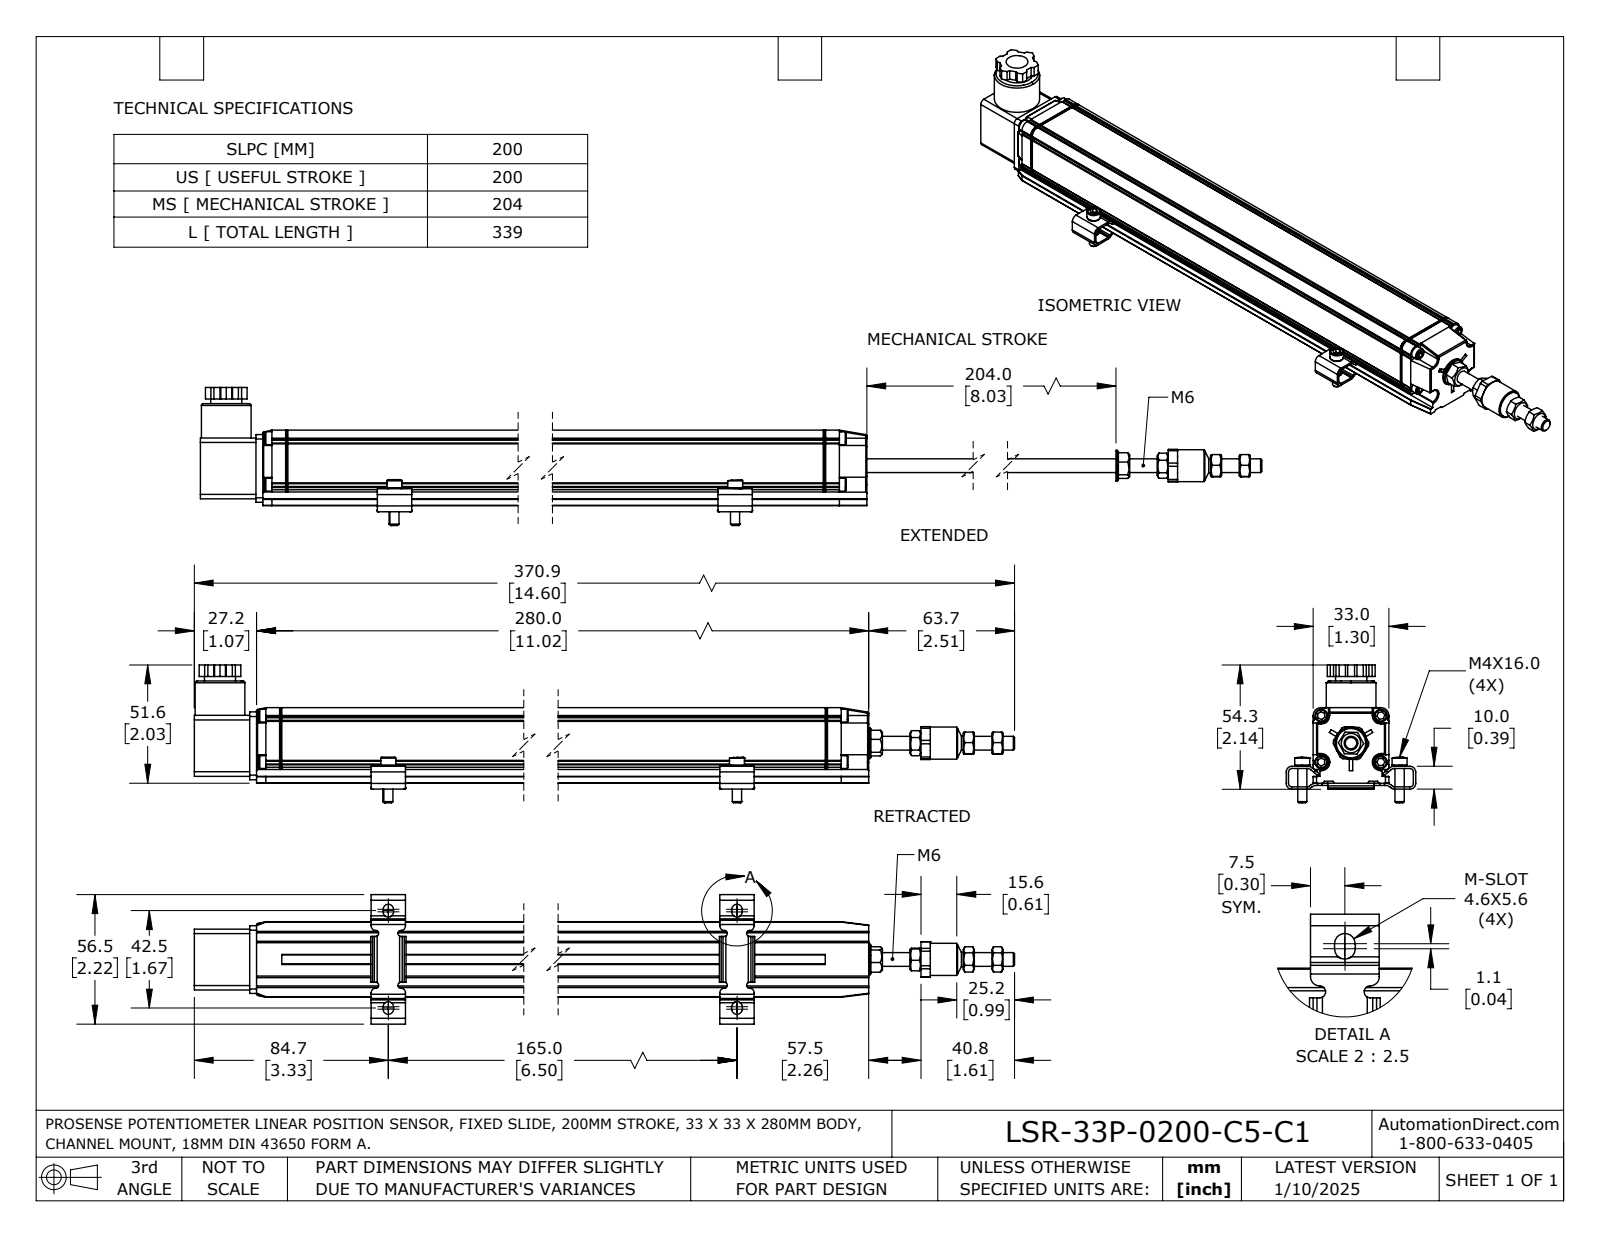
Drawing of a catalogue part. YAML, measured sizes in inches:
part_name: "LSR-33P-0200-C5-C1"
step_written_by: "SolidWorks 2023 (AUTOMOTIVE_DESIGN)"
units: inches
bodies: {solids: 14, faces: 995, planar: 641, cylindrical: 269, other: 85}
overall_size: [14.6, 2.37, 2.224]
volume: 17.97
surface_area: 130.1
round_holes:
  - {diameter: 0.106, count: 4}
  - {diameter: 0.13, count: 4}
  - {diameter: 0.169, count: 1}
  - {diameter: 0.205, count: 1}
  - {diameter: 0.209, count: 1}
  - {diameter: 0.232, count: 1}
  - {diameter: 0.276, count: 1}
  - {diameter: 0.285, count: 1}
  - {diameter: 0.394, count: 1}
  - {diameter: 0.413, count: 1}
  - {diameter: 0.573, count: 1}
  - {diameter: 0.602, count: 1}
round_bosses_or_shafts:
  - {diameter: 0.157, count: 5}
  - {diameter: 0.118, count: 5}
  - {diameter: 0.256, count: 4}
  - {diameter: 0.22, count: 4}
  - {diameter: 0.854, count: 1}
  - {diameter: 0.551, count: 1}
  - {diameter: 0.535, count: 1}
  - {diameter: 0.528, count: 1}
partial_cylinders:
  - {radius: 0.079, count: 28}
  - {radius: 0.02, count: 23}
  - {radius: 0.008, count: 16}
  - {radius: 0.051, count: 8}
  - {radius: 0.059, count: 8}
  - {radius: 0.089, count: 8}
  - {radius: 0.118, count: 8}
  - {radius: 0.039, count: 4}
face_to_face_distances: [1.299, 0.118, 0.039, 0.22, 1.181, 1.079, 0.079, 0.102, 0.142, 0.063]
hole_center_spacings: [0.047, 0.583, 0.607, 0.696, 0.73, 0.799, 1.024, 1.299]
